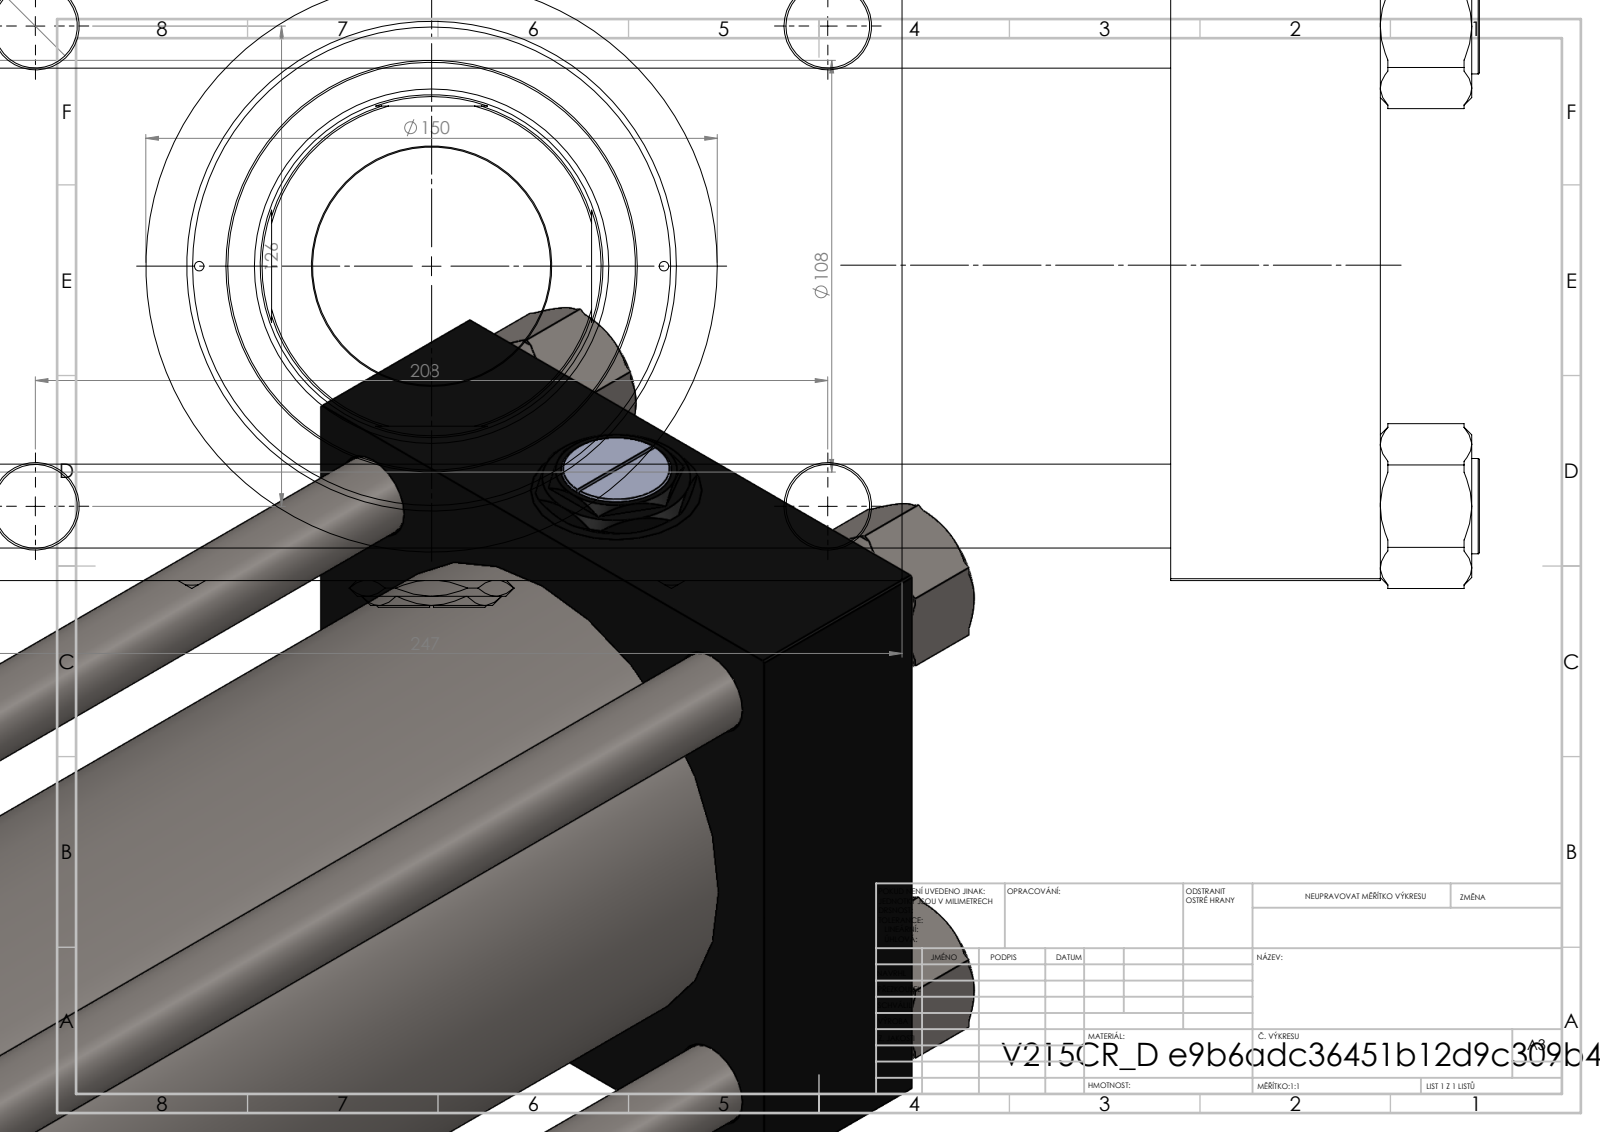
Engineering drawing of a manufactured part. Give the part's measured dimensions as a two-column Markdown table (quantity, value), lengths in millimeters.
| quantity | value |
| --- | --- |
| part name | V215CR_D_TYCINKA; V215_VC_A; NUT_M5_D; V215CR_VCP_D (+2 more) |
| STEP written by | SolidWorks 2019 (CONFIG_CONTROL_DESIGN) |
| units | millimeters |
| bodies | 13 solids, 1250 faces (593 planar, 97 cylindrical, 560 other) |
| overall size | 1658 × 247 × 179 |
| volume | 17 720 000 mm³ |
| surface area | 2 465 000 mm² |
| round holes (diameter × count) | 22 × 8, 32.24 × 3, 45 × 3, 2.5 × 2, 7 × 2, 62.5 × 1, 90 × 1, 93 × 1, 96 × 1, 125 × 1, 125.5 × 1 |
| round bosses / shafts (diameter × count) | 25 × 4, 150 × 1, 131 × 1, 108 × 1 |
| partial cylindrical surfaces (radius × count) | 44 × 1 |
| main face-to-face distances | 165, 1464, 55, 1519, 1575, 1520, 56, 41, 206, 1553.74 |
| hole center spacings | 41.05, 62.98, 76.28, 89.02, 121.59, 125.9, 132.47, 139.02 |
